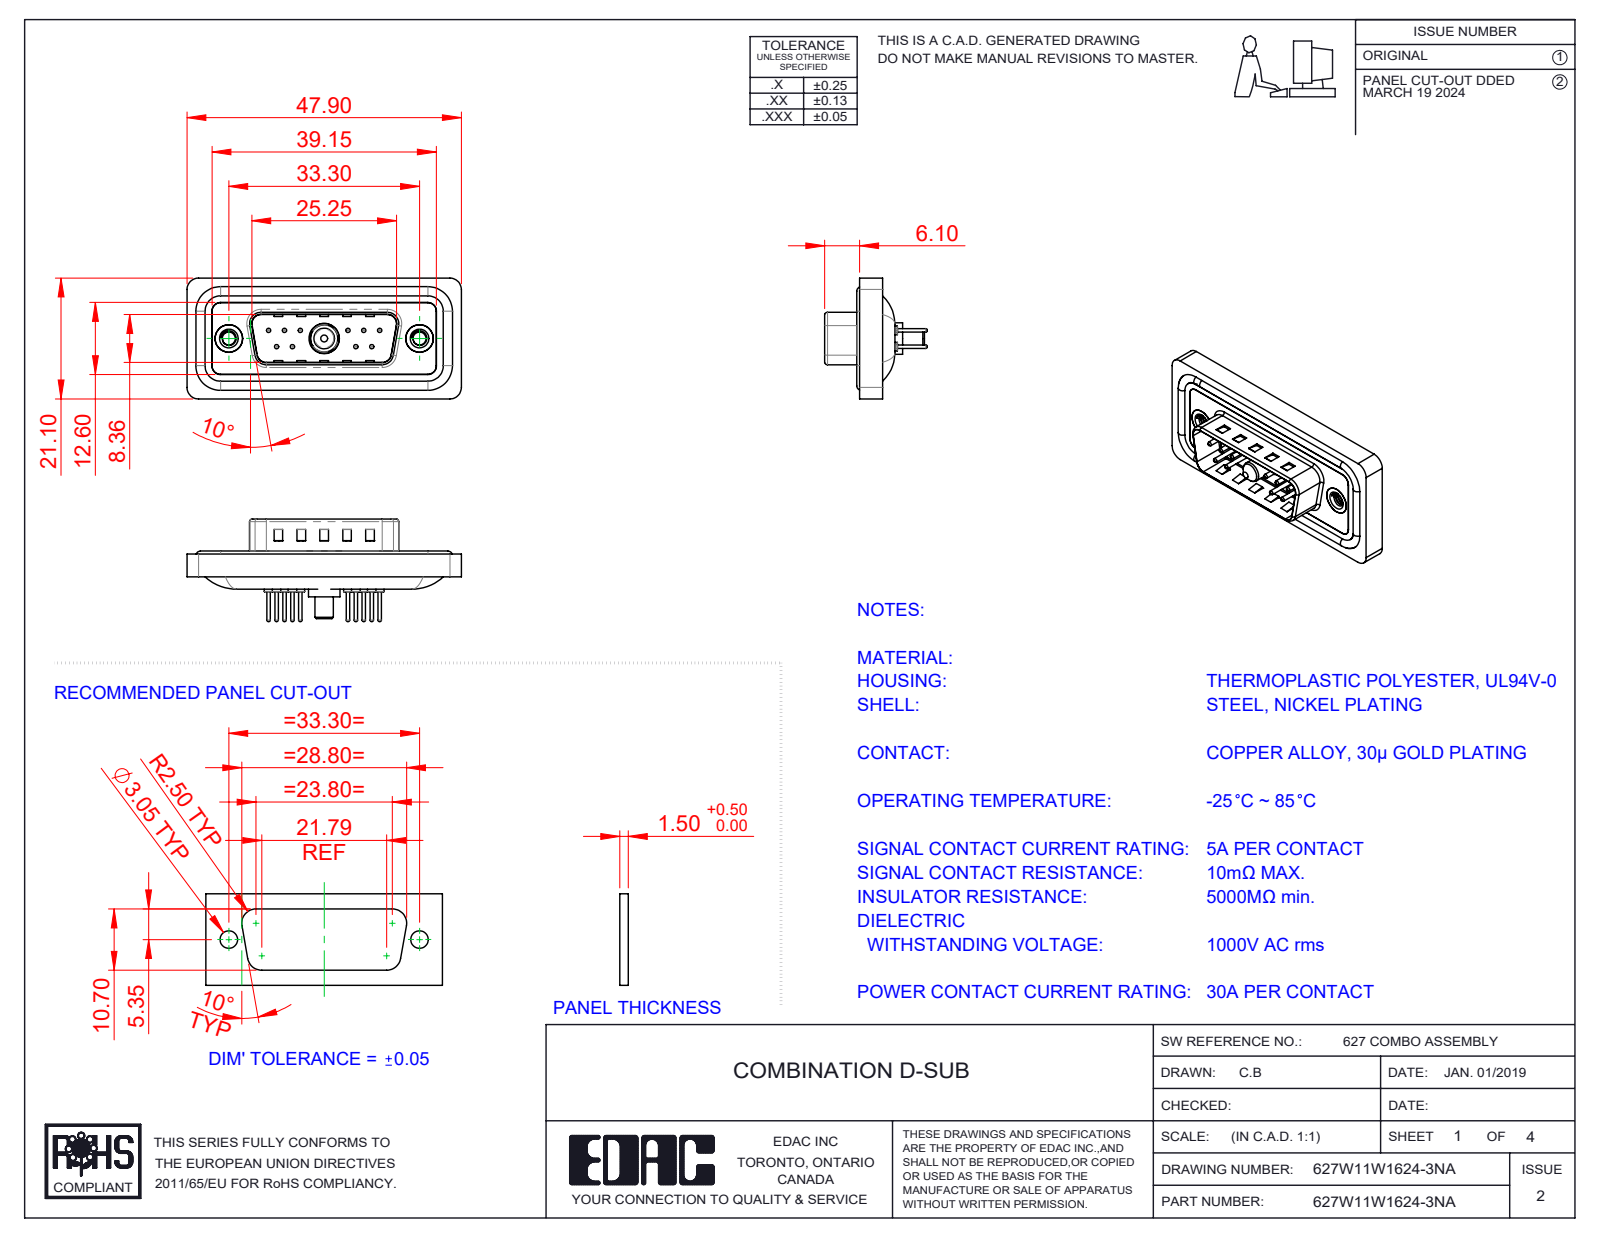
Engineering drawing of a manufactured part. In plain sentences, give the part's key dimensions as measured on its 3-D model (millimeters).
The part is named "627Combo Contact Row 1_24; 627Combo Shell Rear_15 Contacts; 627W11W1624-3NA; 627Combo Threaded Rivet_A (+5 more)". Its 3-D file was written by "SolidWorks 2023 (CONFIG_CONTROL_DESIGN)". It is 19 solids with 867 faces: 266 planar, 349 cylindrical and 252 other. Overall it measures 47.9 by 21.1 by 17.9 millimeters. Its volume is 5 457 cubic millimeters and its surface area 8 838 square millimeters. Round holes: 10 of diameter 0.75, 10 of diameter 1.6, 10 of diameter 2, 2 of diameter 2.26, 2 of diameter 4, 2 of diameter 4.8, 2 of diameter 5, 1 of diameter 4.85, 1 of diameter 5.3. Round bosses or shafts: 10 of diameter 1.5, 10 of diameter 0.6, 4 of diameter 1.6, 2 of diameter 4.9, 1 of diameter 5.5, 1 of diameter 5.2, 1 of diameter 4.75, 1 of diameter 3.75. Partial cylindrical surfaces (rounded edges, fillets, slot ends): 26 of radius 1.5, 20 of radius 2, 8 of radius 0.5, 8 of radius 1.6, 7 of radius 1, 4 of radius 0.25, 4 of radius 0.6, 4 of radius 0.65. The main face-to-face distances are 0.4, 1.1, 1.6, 1.5, 0.5, 2.9, 3.1, 2.5, 4.1, 0.82. The hole center spacings are 3.16, 2.77, 13.85, 11.08, 16.62, 5.03, 5.04, 5.54.
